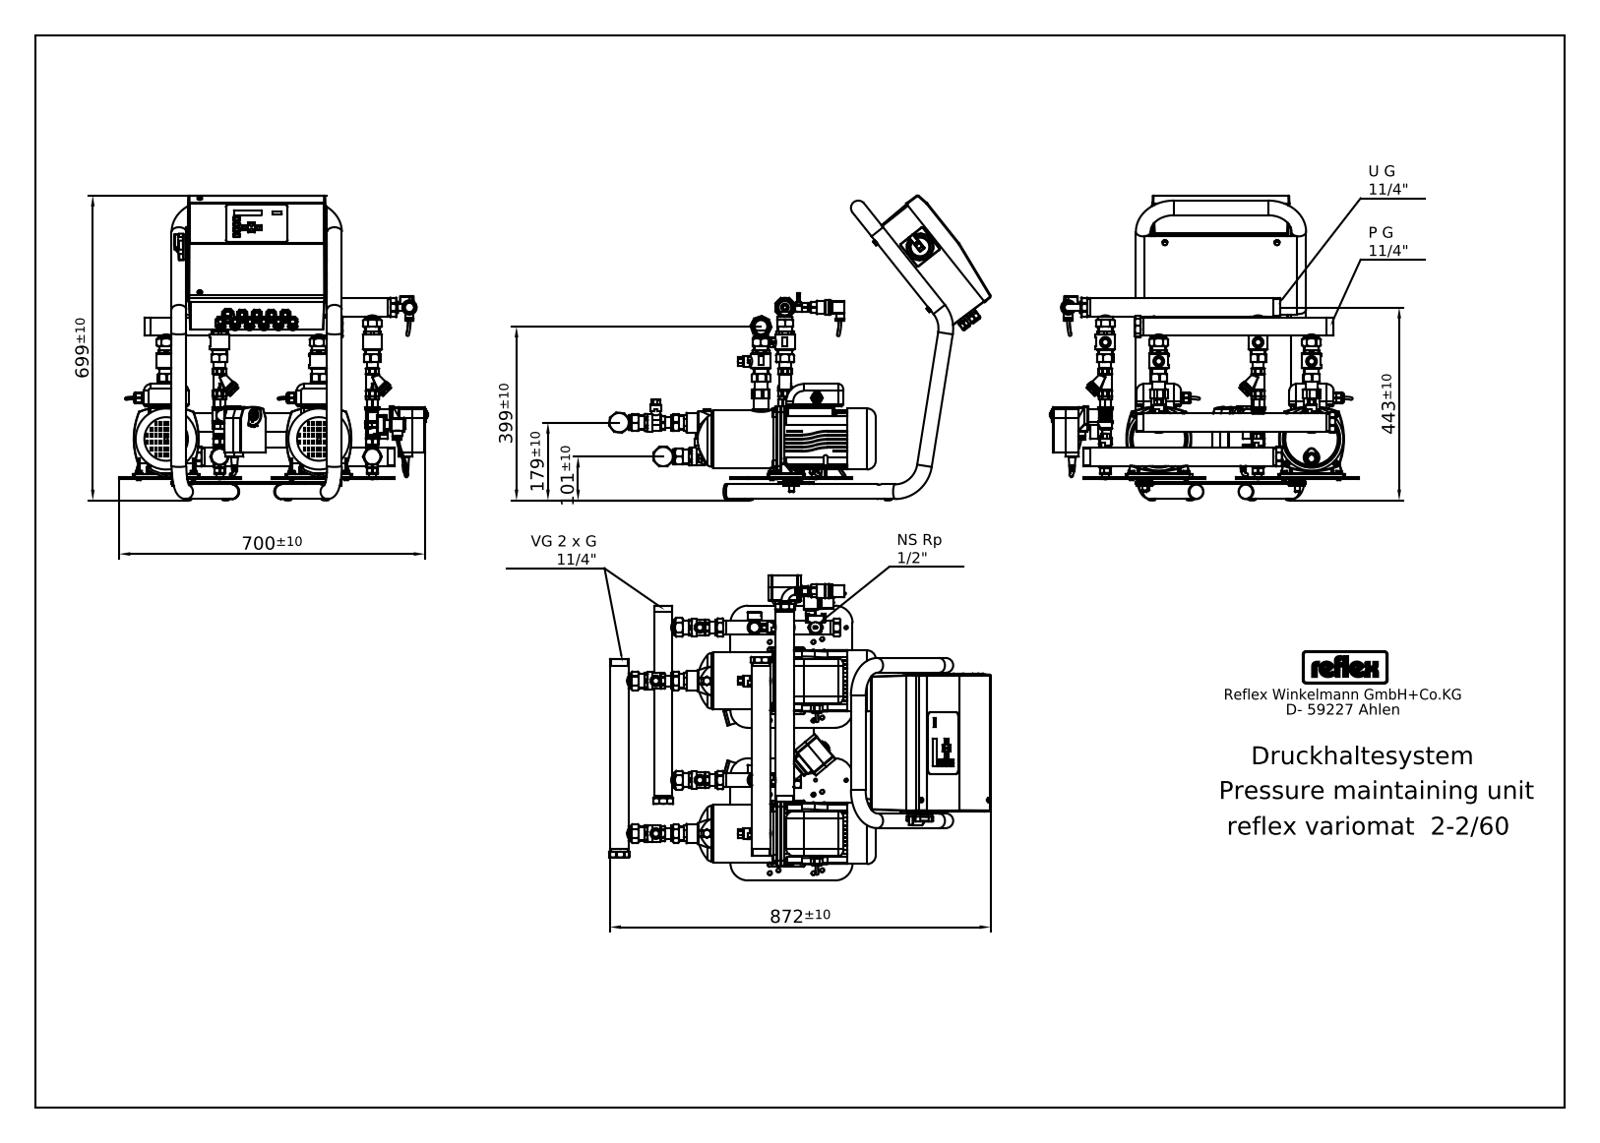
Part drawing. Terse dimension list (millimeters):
written by: Mechanical Desktop 2008 (CONFIG_CONTROL_DESIGN)
unit: mm
bodies: 77 solids, 3414 faces (1947 planar, 943 cylindrical, 524 other)
size: 866.62 × 749.68 × 695
volume: 33 840 000 mm³; area: 2 858 000 mm²
holes: 11× ⌀10.5, 8× ⌀3, 8× ⌀6, 8× ⌀14.5, 4× ⌀8, 2× ⌀27, 2× ⌀38.95, 1× ⌀6.5, 1× ⌀13.5, 1× ⌀45
bosses: 20× ⌀20, 14× ⌀33.7, 12× ⌀19, 12× ⌀8, 10× ⌀17.5, 9× ⌀24.5, 8× ⌀20.6, 8× ⌀11.63
rounds: 66× R1, 39× R5, 10× R105, 8× R2, 8× R3, 8× R4.5, 8× R5.1, 8× R10.5
face distances: 4, 2, 2.01, 6, 10, 16, 12, 17.5, 143.98, 279.95
hole spacings: 32.07, 350, 33, 56.63, 66, 86.96, 99, 16.86
